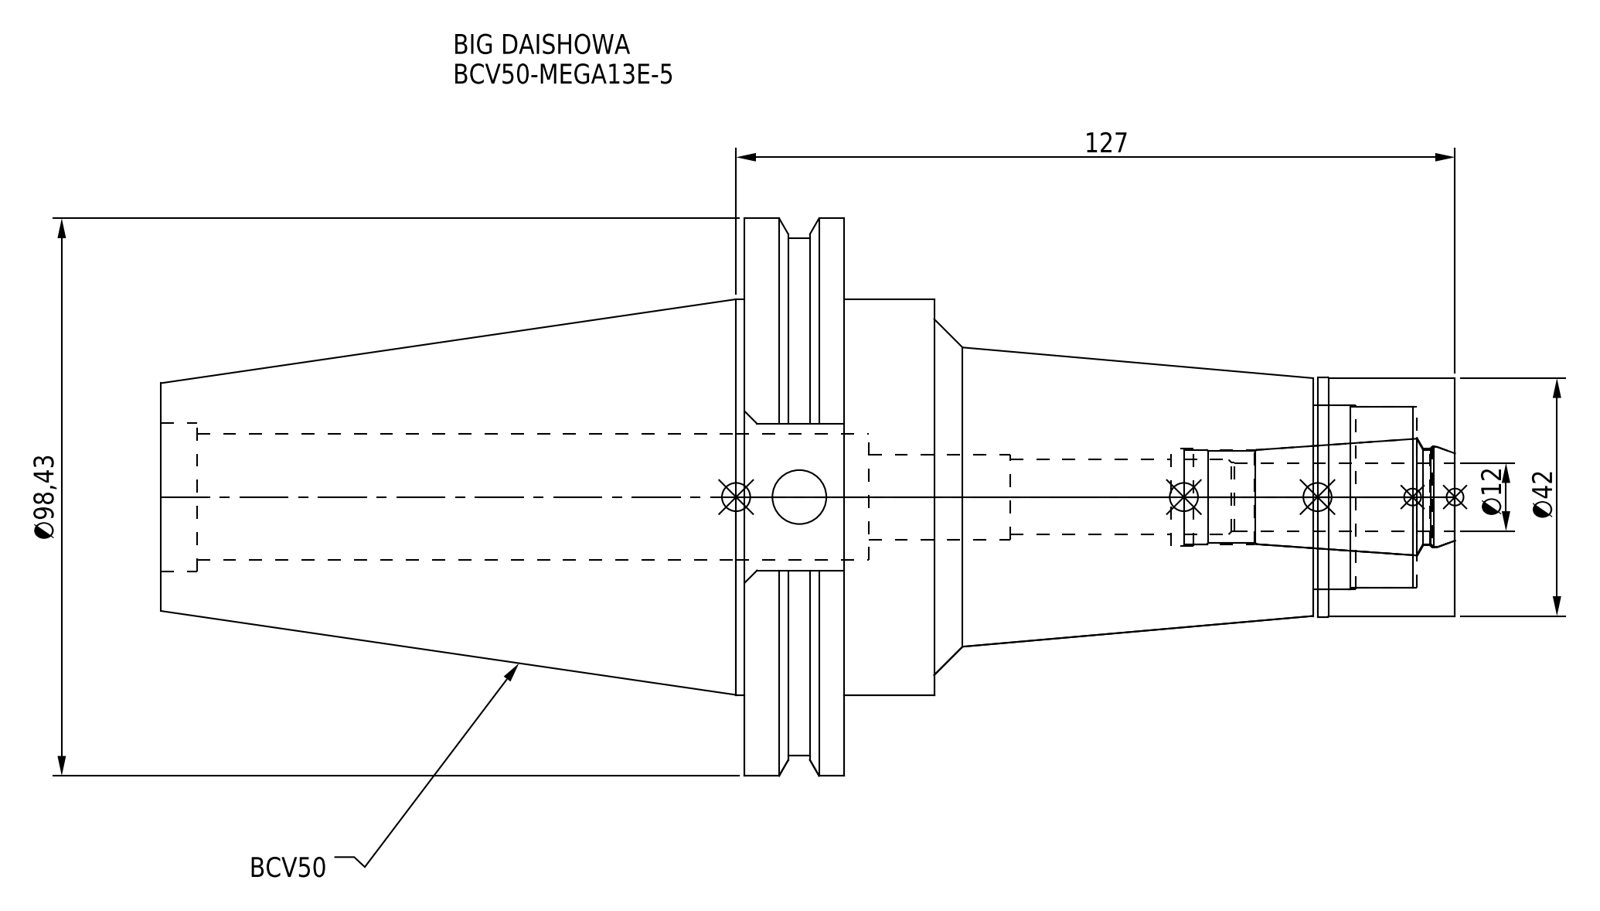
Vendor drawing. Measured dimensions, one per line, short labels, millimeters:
name: BCV50-MEGA13E-5; MEN13_1.stp; BCV50-MEGA13E-5-120-FreeParts; BCV50-MEGA13E-5_1.stp (+3 more)
written by: SolidWorks 2019 (CONFIG_CONTROL_DESIGN)
unit: mm
bodies: 2 solids, 93 faces (31 planar, 42 cylindrical, 20 other)
size: 228.6 × 98.42 × 94.95
volume: 518 383 mm³; area: 71 653 mm²
holes: 1× ⌀9.53, 1× ⌀13.3, 1× ⌀15, 1× ⌀16.6, 1× ⌀17, 1× ⌀17.2, 1× ⌀17.9, 1× ⌀22.3, 1× ⌀26.23, 1× ⌀32, 1× ⌀32.5
bosses: 1× ⌀98.42, 1× ⌀91.29, 1× ⌀69.85, 1× ⌀42.3, 1× ⌀42
face distances: 17.55, 107.95, 125.5, 92, 15.95, 33.5, 228.6, 136.6, 120.65, 103.1
